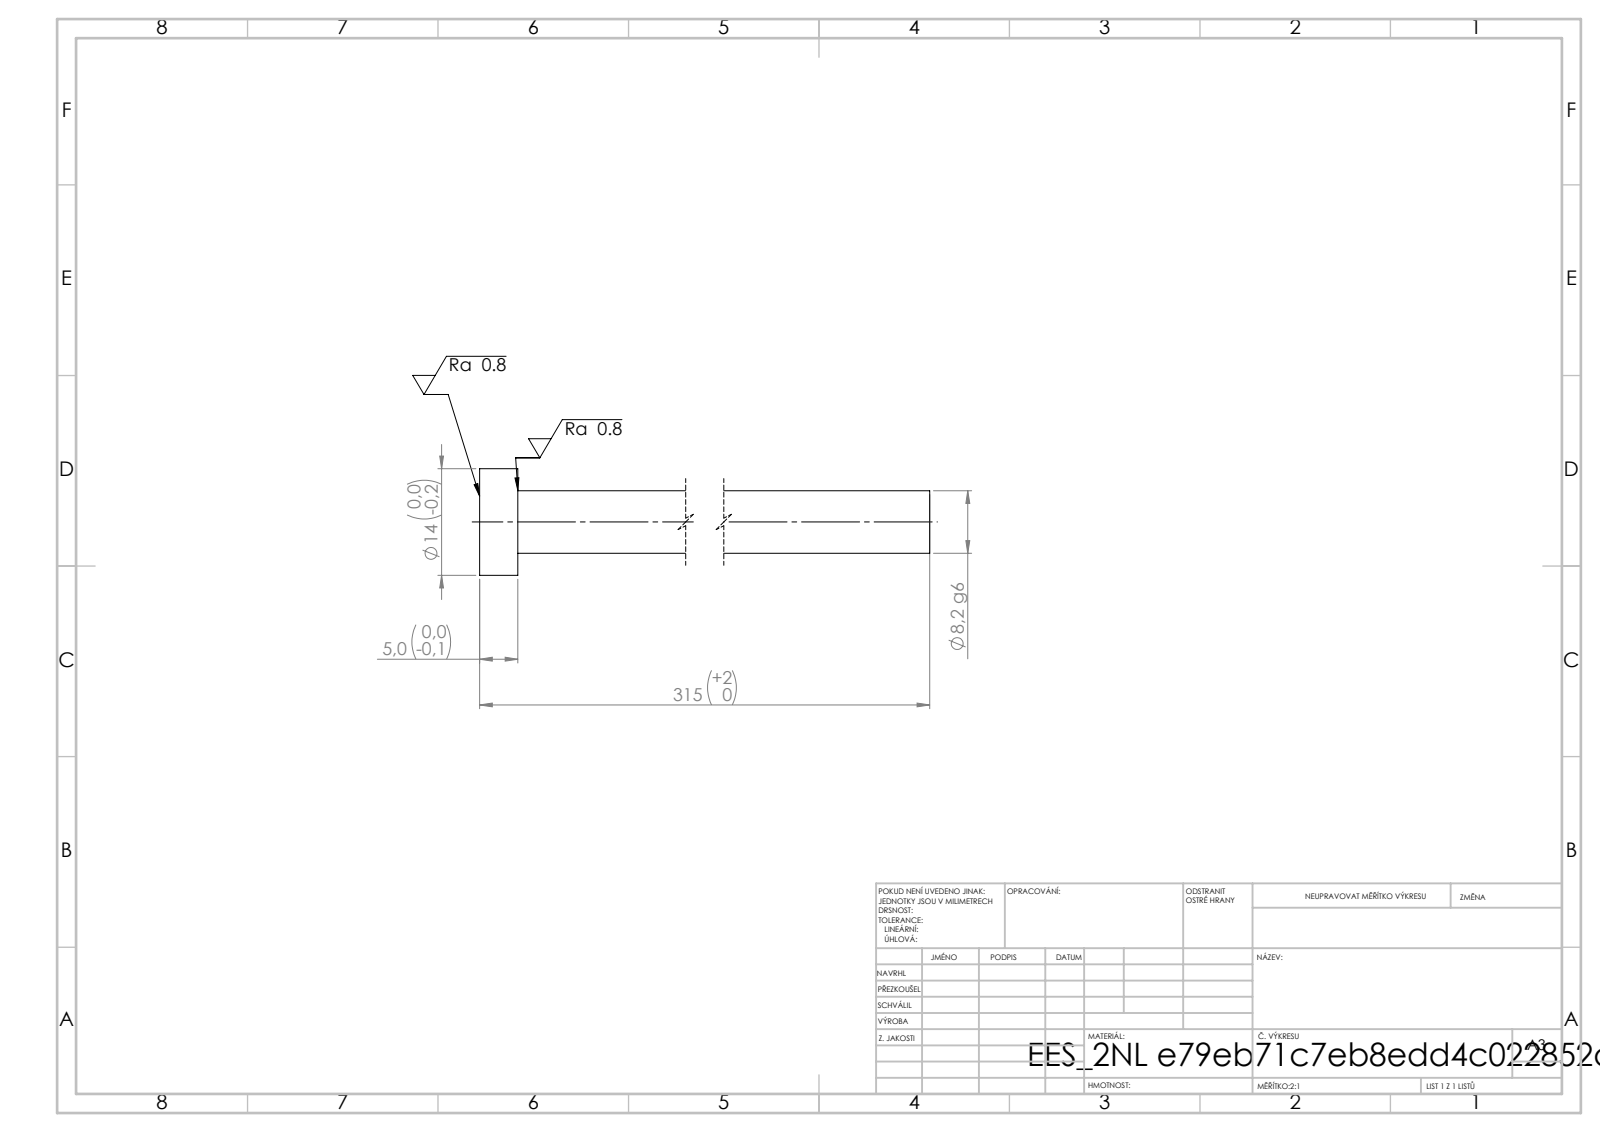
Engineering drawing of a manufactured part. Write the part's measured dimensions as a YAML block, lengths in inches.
step_written_by: "SolidWorks 2019 (CONFIG_CONTROL_DESIGN)"
units: inches
bodies: {solids: 1, faces: 7, planar: 3, cylindrical: 4, other: 0}
overall_size: [12.402, 0.551, 0.551]
volume: 1.046
surface_area: 13.2
round_bosses_or_shafts:
  - {diameter: 0.551, count: 1}
  - {diameter: 0.323, count: 1}
face_to_face_distances: [0.197, 12.402, 12.205]
